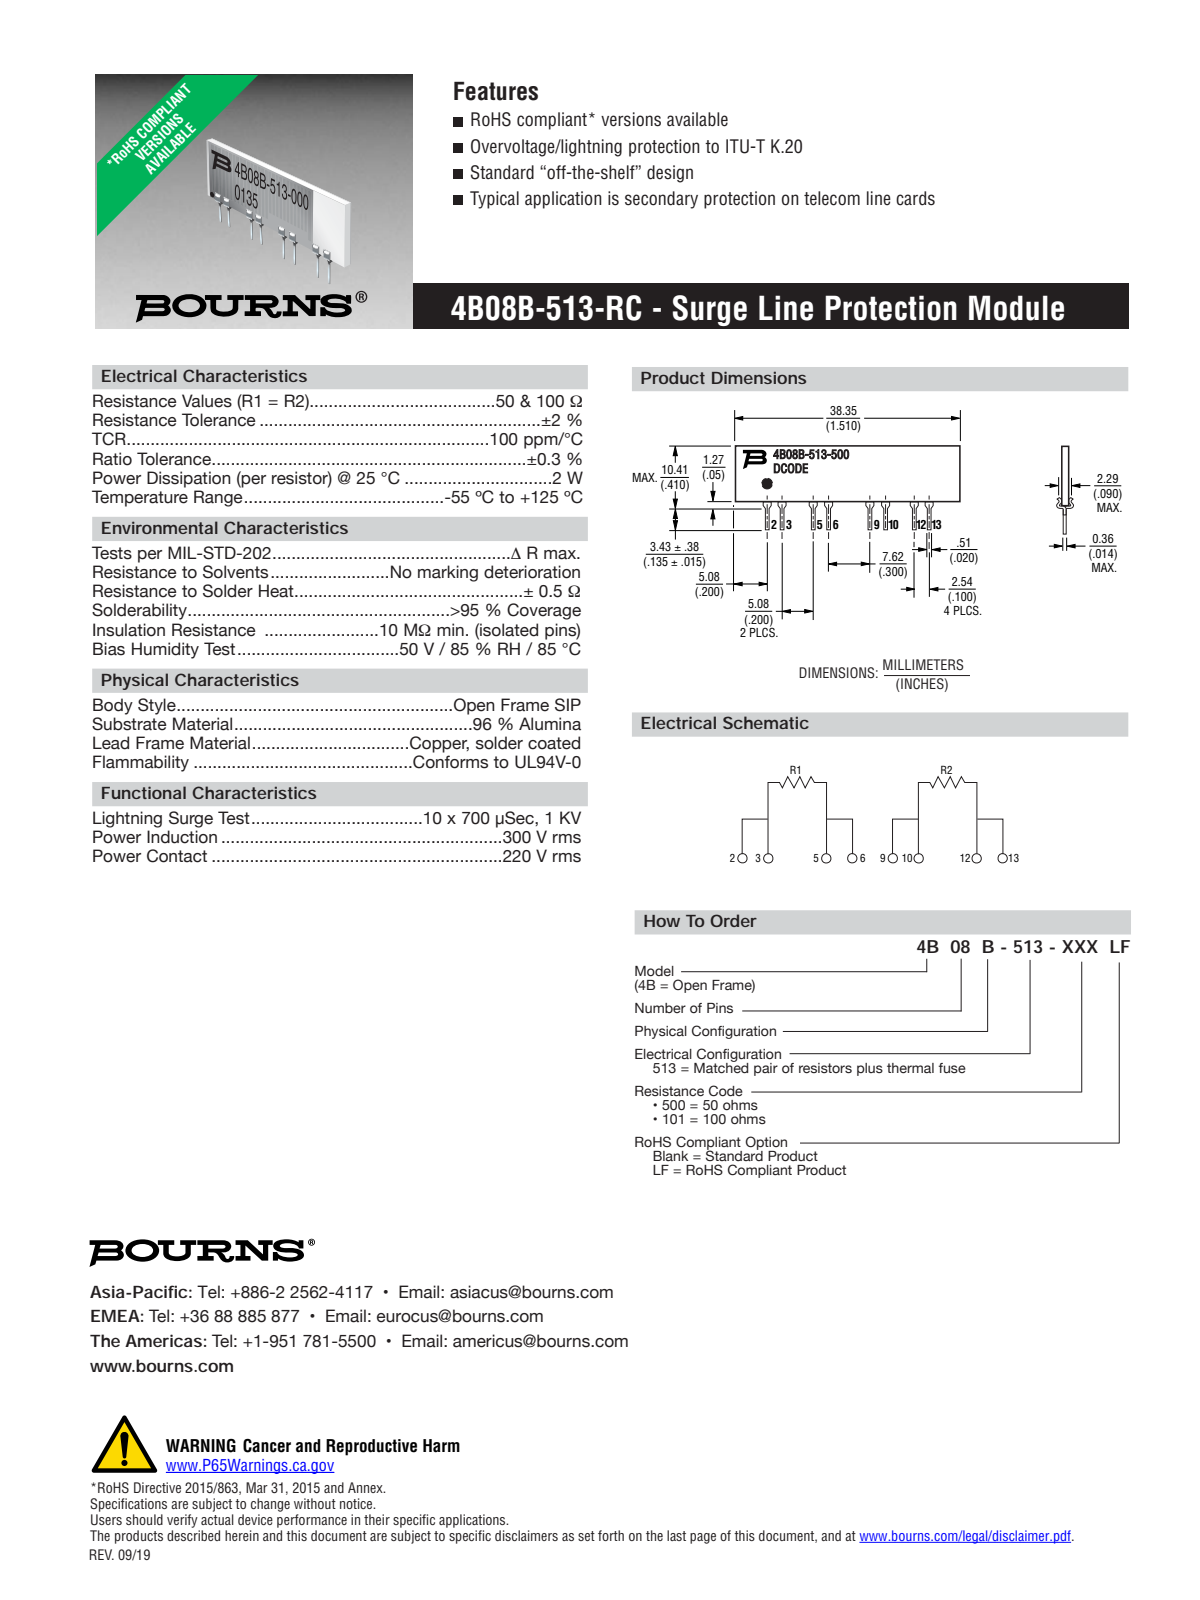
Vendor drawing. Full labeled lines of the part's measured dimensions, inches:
Part name (STEP PRODUCT): 4B08B-513-RC
STEP written by: PRO/ENGINEER BY PARAMETRIC TECHNOLOGY CORPORATION, 2010100 (CONFIG_CONTROL_DESIGN)
Units: inches
Bodies: 1 solid, 174 faces (142 planar, 32 cylindrical, 0 other)
Overall size (bounding box): 1.51 × 0.545 × 0.09
Volume: 0.033 in³ · Surface area: 1.45 in²
Partial cylindrical surfaces — rounded edges, fillets, slot ends (radius × count): R0.008 ×4
Main face-to-face distances: 0.06, 0.36, 0.023, 0.037, 0.014, 1.51, 0.02, 0.015, 0.038, 0.052
